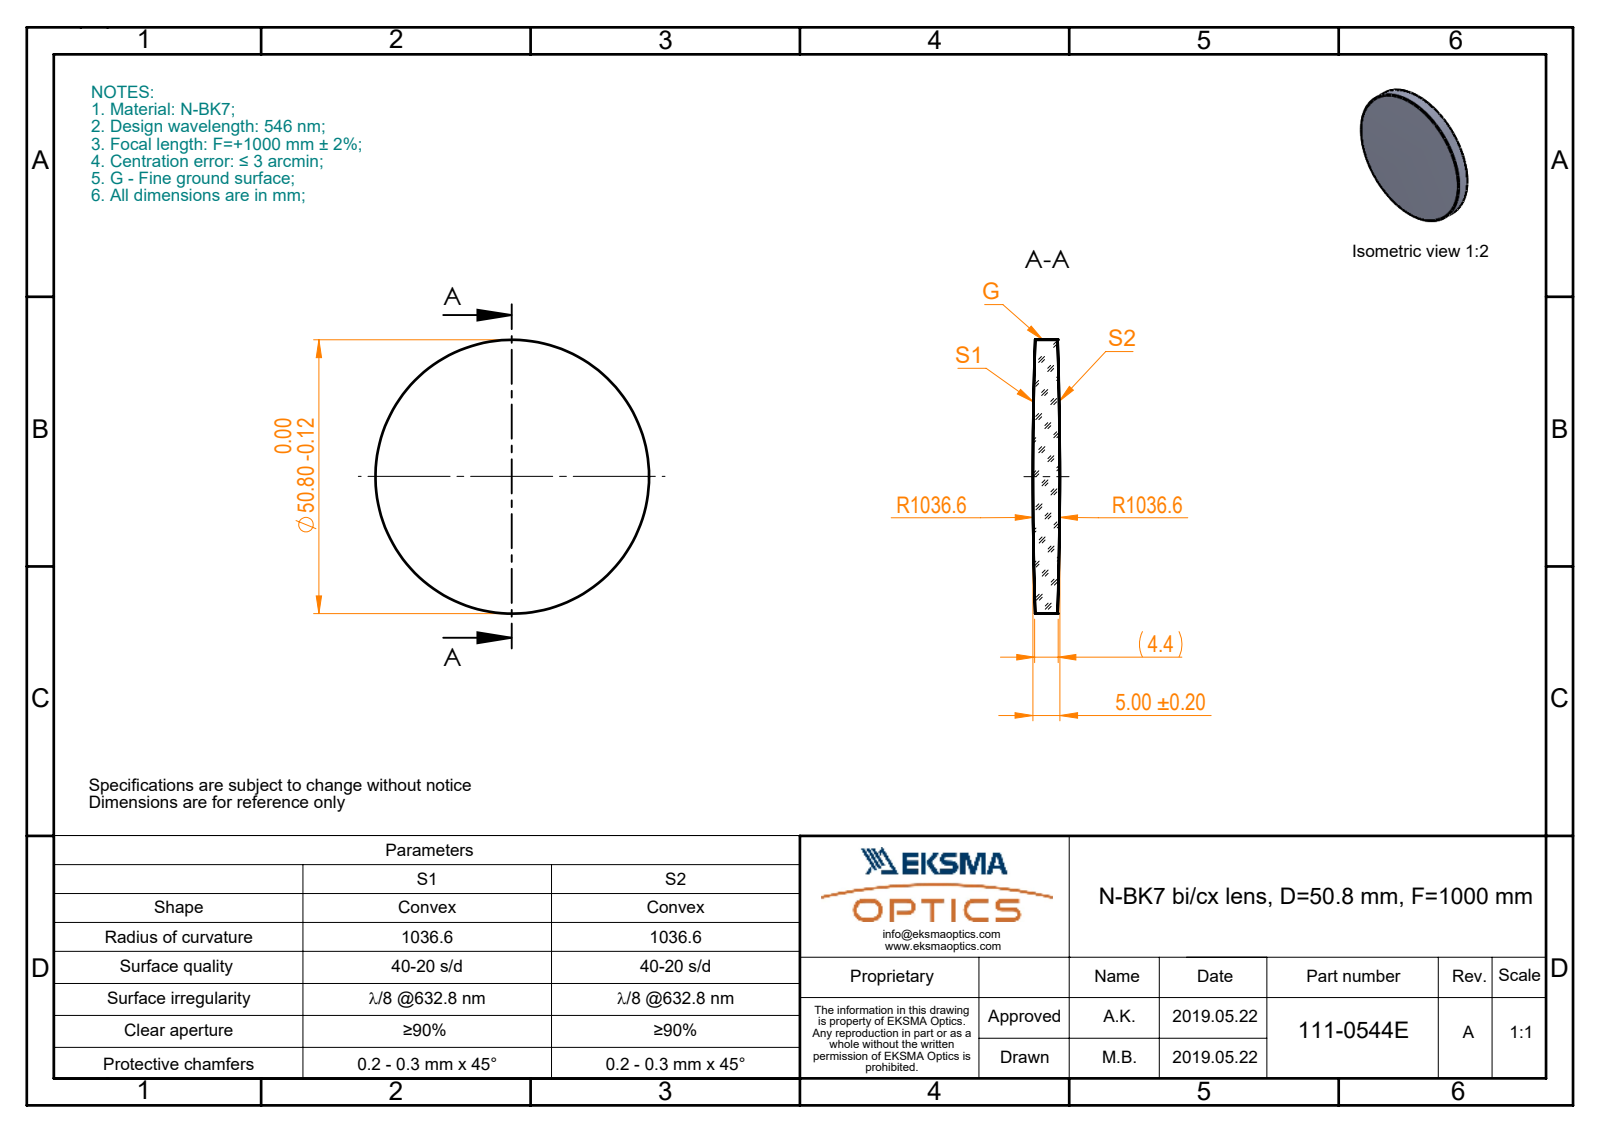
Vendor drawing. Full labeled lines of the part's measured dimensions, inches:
Part name (STEP PRODUCT): 111-0544E BK7 bi-cx 50.8 F1000
STEP written by: SolidWorks 2017 (CONFIG_CONTROL_DESIGN)
Units: inches
Bodies: 1 solid, 6 faces (0 planar, 2 cylindrical, 4 other)
Overall size (bounding box): 2 × 2 × 0.197
Volume: 0.58 in³ · Surface area: 7.367 in²
Round bosses / shafts (diameter × count): ⌀2 ×1
